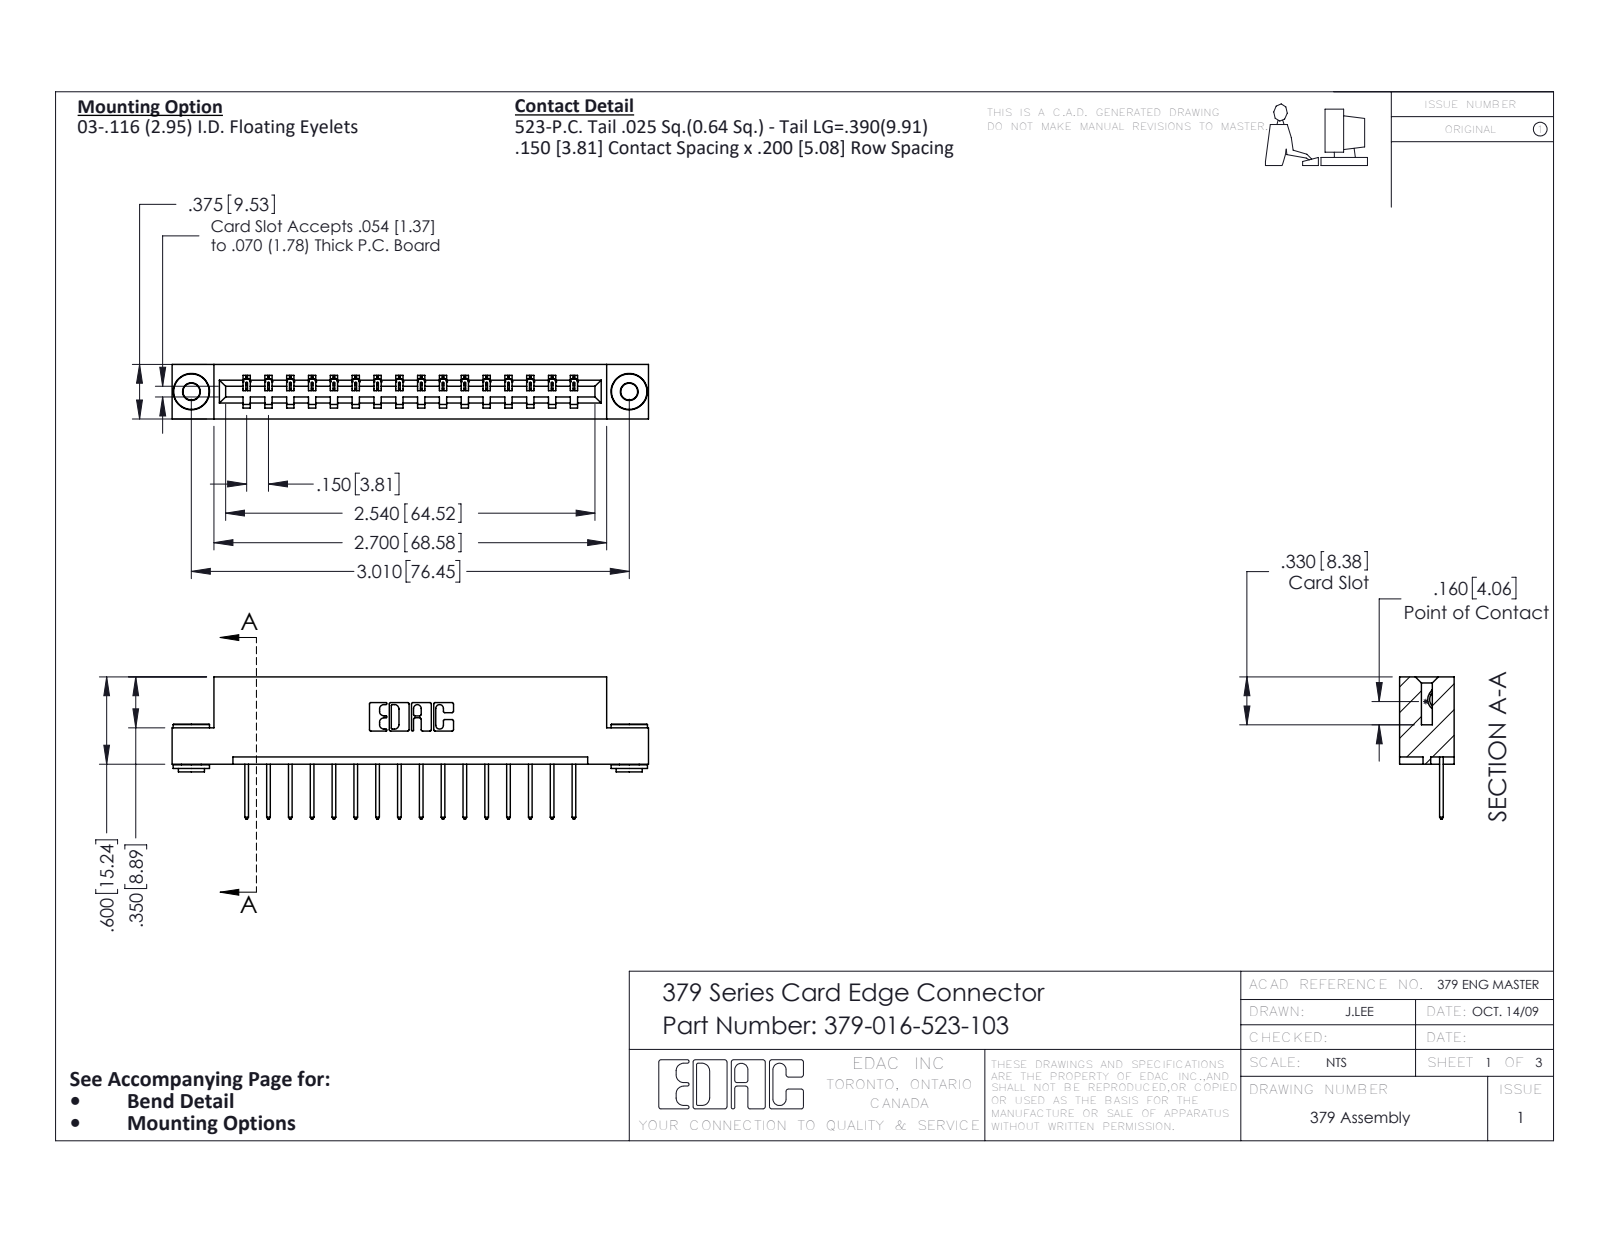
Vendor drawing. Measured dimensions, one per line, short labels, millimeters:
name: 345-292-001_345-293-123; 379-016-523-103; 379 Part_Flush - .156 Dia - TH; 345-250-002_345-250-002-102
written by: SolidWorks 2020 (CONFIG_CONTROL_DESIGN)
unit: mm
bodies: 19 solids, 1080 faces (752 planar, 320 cylindrical, 8 other)
size: 83.2 × 24.8 × 9.5
volume: 8 440 mm³; area: 8 755 mm²
holes: 2× ⌀2.9, 2× ⌀4
bosses: 2× ⌀6.4, 2× ⌀4.6, 2× ⌀3.5
rounds: 32× R0.2, 32× R0.3, 22× R0.3, 6× R0.2, 6× R0.8, 3× R0.7, 1× R0.4, 1× R0.6
face distances: 7.6, 1.9, 9.5, 15.2, 3.8, 5.7, 5.1, 11.4, 7, 19.1
hole spacings: 76.5
